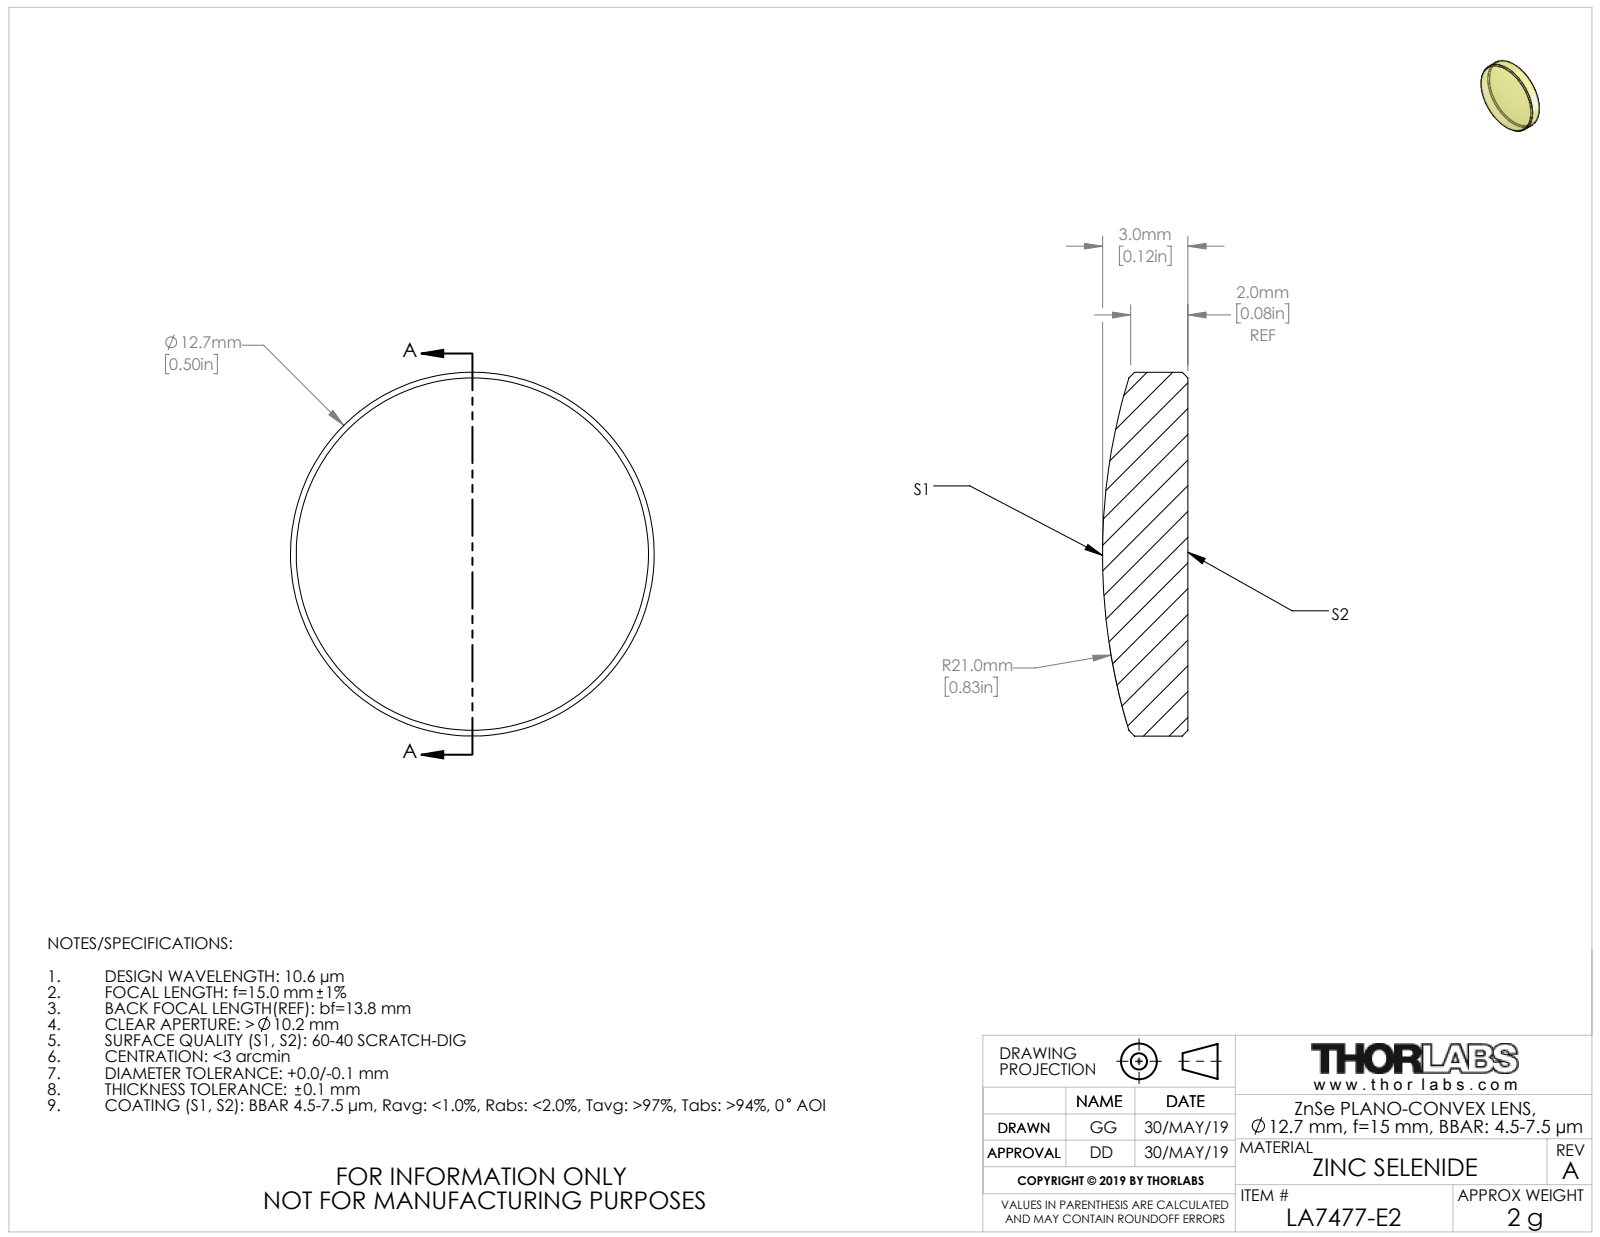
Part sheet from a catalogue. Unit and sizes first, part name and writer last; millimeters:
Units: millimetres
Overall size (bounding box): 12.7 × 12.7 × 2.98
Round bosses / shafts (diameter × count): ⌀12.7 ×1
Volume: 315 mm³ · Surface area: 329 mm²
Bodies: 1 solid, 9 faces (1 planar, 2 cylindrical, 6 other)
Part name (STEP PRODUCT): TTN047574-E0W
STEP written by: SolidWorks 2018 (CONFIG_CONTROL_DESIGN)
